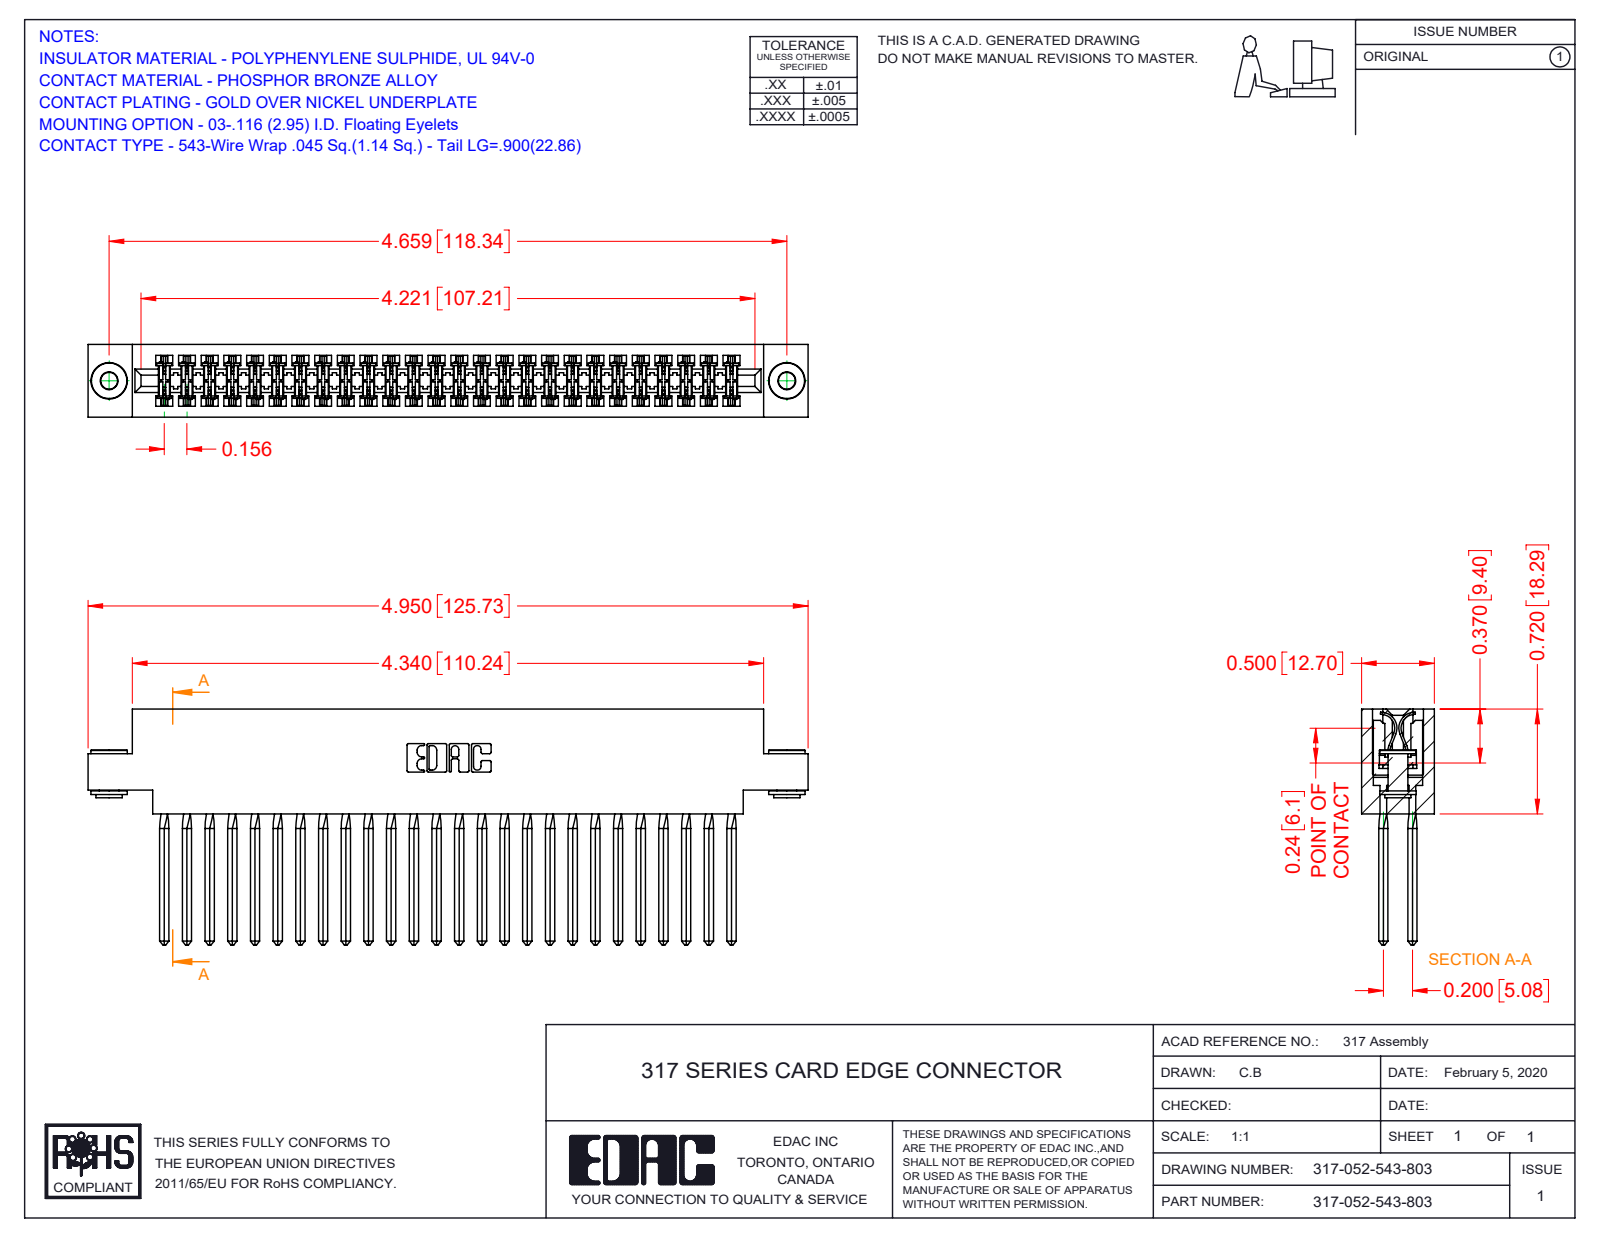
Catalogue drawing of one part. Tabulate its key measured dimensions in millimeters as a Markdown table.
| quantity | value |
| --- | --- |
| part name | 317-052-543-803; 317 Part_.156 Dia - TH; 345-250-002_345-250-002-102; 317-290-001_543 |
| STEP written by | SolidWorks 2016 (CONFIG_CONTROL_DESIGN) |
| units | millimeters |
| bodies | 55 solids, 4768 faces (3864 planar, 688 cylindrical, 216 other) |
| overall size | 125.7 × 41.1 × 12.7 |
| volume | 20 840 mm³ |
| surface area | 31 200 mm² |
| round holes (diameter × count) | 2.9 × 2, 4 × 2 |
| round bosses / shafts (diameter × count) | 6.4 × 2, 4.6 × 2, 3.5 × 2 |
| partial cylindrical surfaces (radius × count) | 0.4 × 104, 0.3 × 22, 0.2 × 6, 0.8 × 6, 0.7 × 3, 2.4 × 2, 2.5 × 2, 2.8 × 2 |
| main face-to-face distances | 12.7, 1.9, 10.8, 2.8, 8.9, 5, 2.4, 18.3, 5.1, 2.9 |
| hole center spacings | 118.3 |
